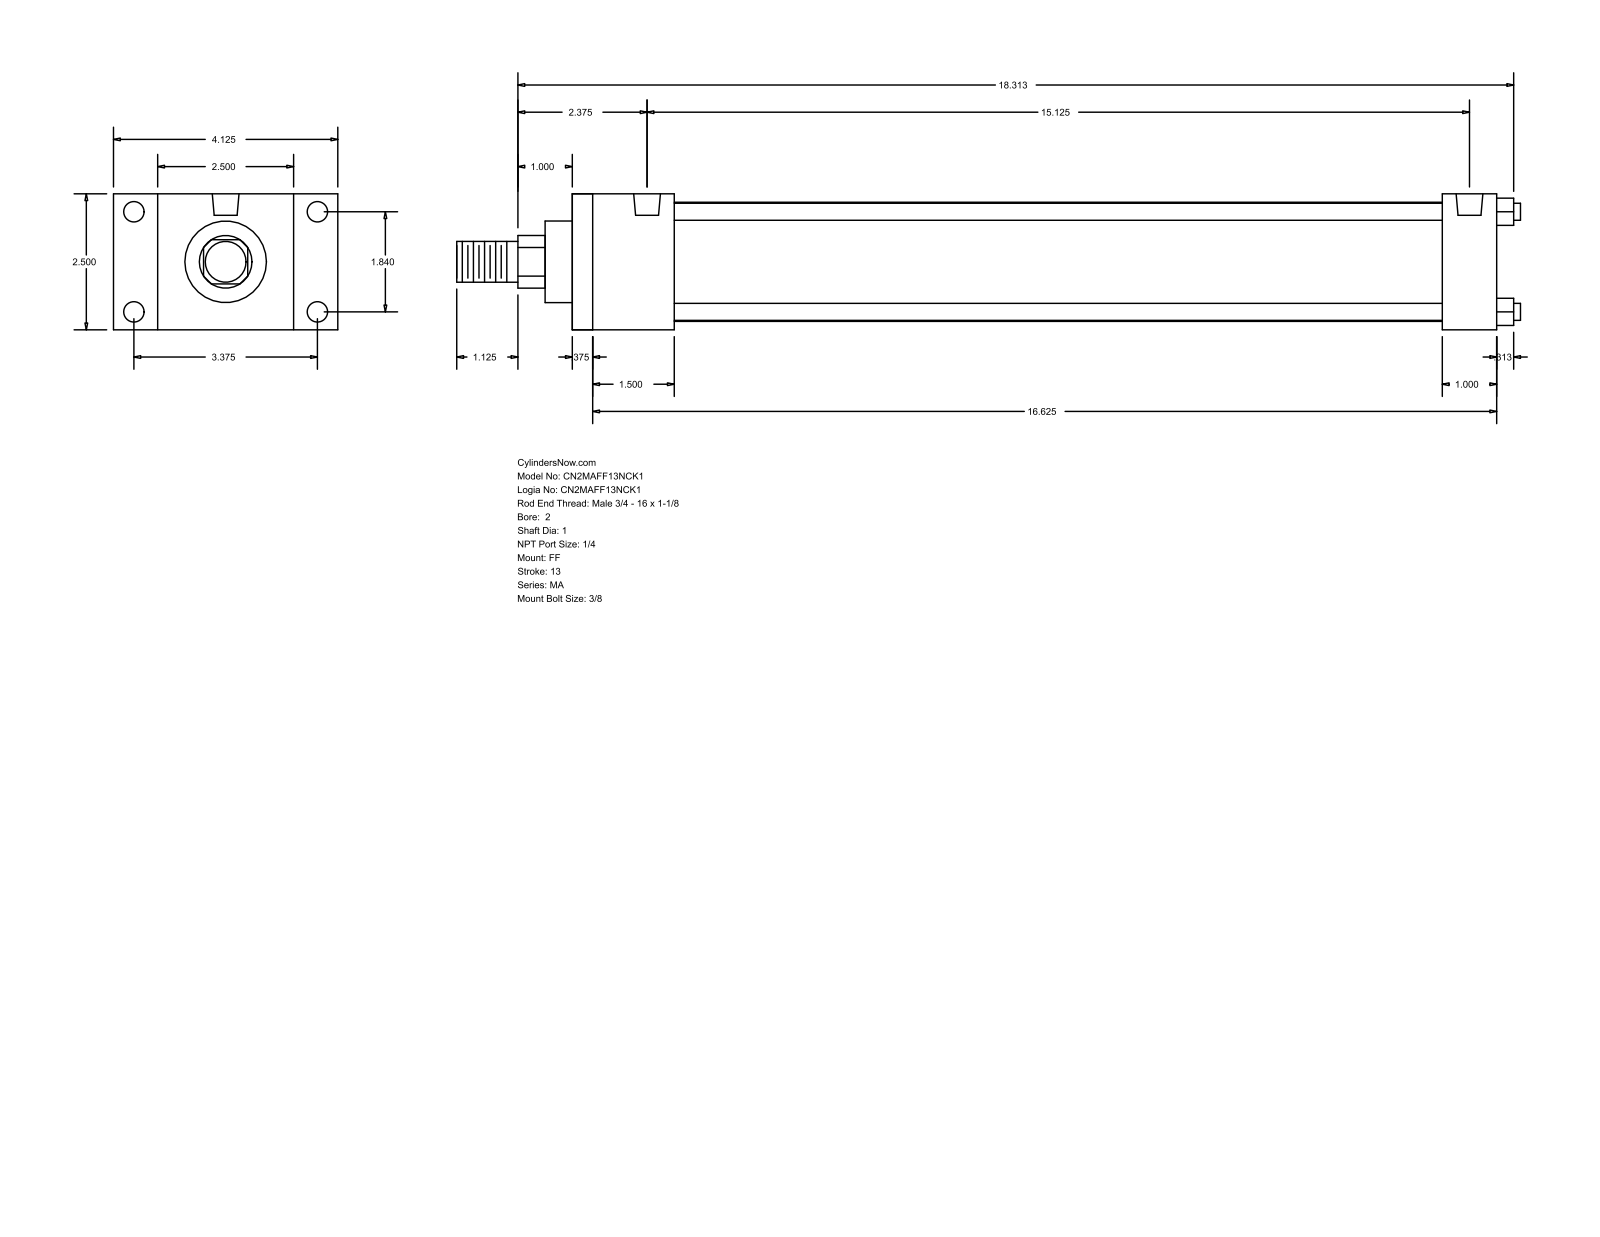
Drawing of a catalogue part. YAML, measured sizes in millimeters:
part_name: "MA_FF__0200_1"
step_written_by: "GSSL Pune (CONFIG_CONTROL_DESIGN)"
units: millimeters
bodies: {solids: 0, faces: 92, planar: 64, cylindrical: 28, other: 0}
overall_size: [496.89, 104.78, 63.5]
round_holes:
  - {diameter: 7.94, count: 4}
  - {diameter: 9.53, count: 4}
  - {diameter: 12.49, count: 2}
round_bosses_or_shafts:
  - {diameter: 7.94, count: 4}
  - {diameter: 55.63, count: 1}
  - {diameter: 38.1, count: 1}
  - {diameter: 25.4, count: 1}
  - {diameter: 19.05, count: 1}
partial_cylinders:
  - {radius: 12.29, count: 1}
face_to_face_distances: [63.5, 431.8, 9.52, 422.28, 25.4, 20.64, 12.7, 47.63, 406.4, 38.11]
hole_center_spacings: [46.74, 85.72, 97.63, 384.17]
